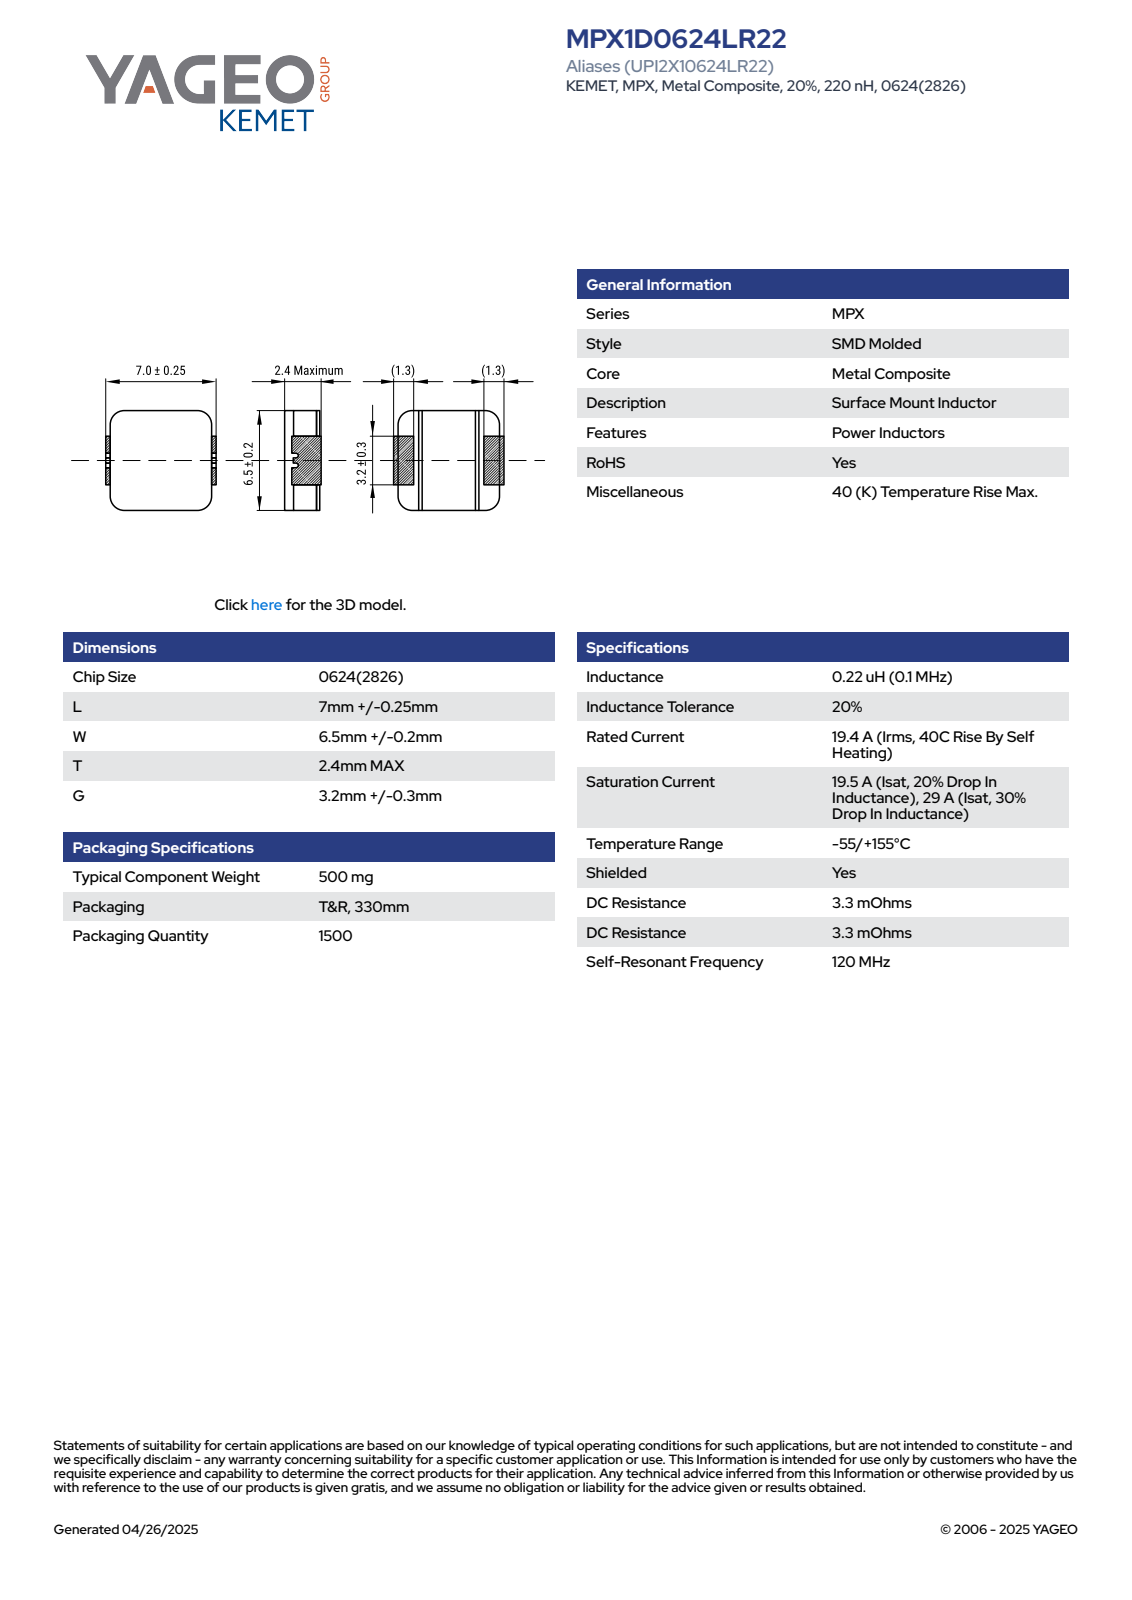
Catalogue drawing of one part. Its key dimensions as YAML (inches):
part_name: "MPX1D0624M(KEMET)"
step_written_by: "SolidWorks 2018 (AUTOMOTIVE_DESIGN)"
units: inches
bodies: {solids: 1, faces: 138, planar: 117, cylindrical: 21, other: 0}
overall_size: [0.285, 0.264, 0.097]
volume: 0.007
surface_area: 0.271
partial_cylinders:
  - {radius: 0.008, count: 4}
  - {radius: 0.039, count: 4}
  - {radius: 0.039, count: 4}
  - {radius: 0.006, count: 3}
face_to_face_distances: [0.094, 0.264, 0.089, 0.275, 0.276, 0.265, 0.097, 0.286, 0.265, 0.063]
